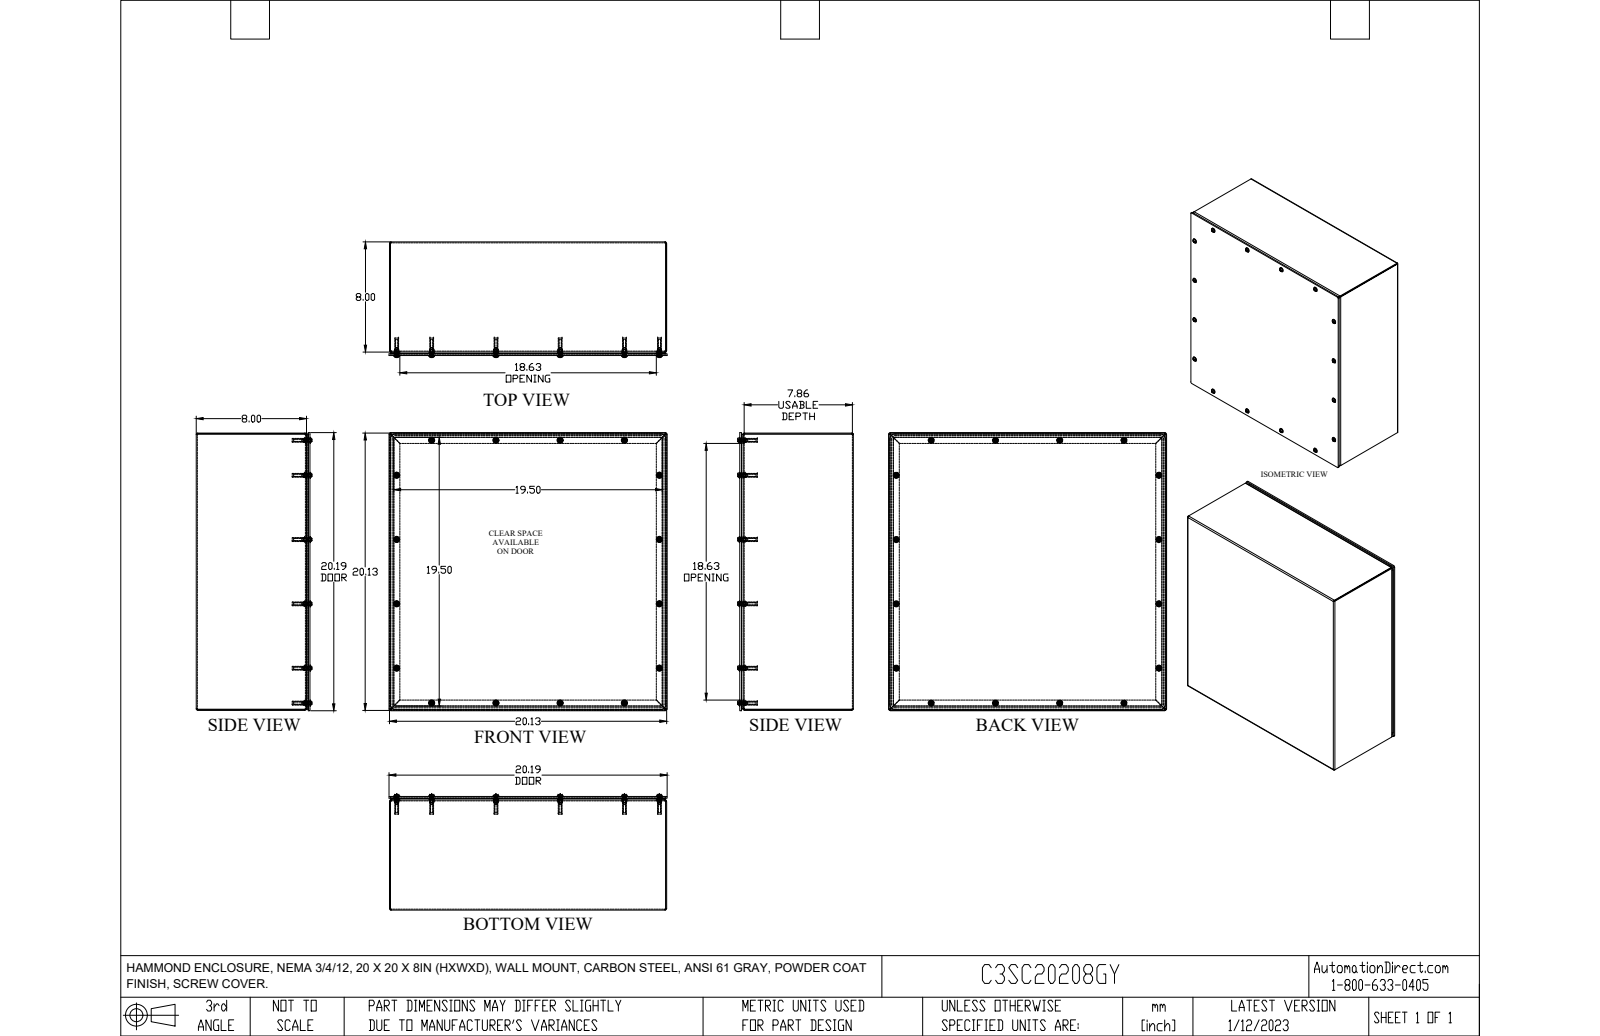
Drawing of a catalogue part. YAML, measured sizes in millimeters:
part_name: "C3SC20208GY"
step_written_by: "SolidWorks 2021 (AUTOMOTIVE_DESIGN)"
units: millimeters
bodies: {solids: 51, faces: 1476, planar: 920, cylindrical: 272, other: 284}
overall_size: [512.8, 512.8, 213.4]
volume: 2129000
surface_area: 2028000
round_holes:
  - {diameter: 4, count: 16}
  - {diameter: 4.1, count: 16}
  - {diameter: 6.4, count: 16}
round_bosses_or_shafts:
  - {diameter: 11.2, count: 16}
  - {diameter: 9.9, count: 16}
  - {diameter: 7, count: 16}
  - {diameter: 6.1, count: 16}
  - {diameter: 4.8, count: 16}
  - {diameter: 3.8, count: 16}
partial_cylinders:
  - {radius: 4.1, count: 16}
  - {radius: 1, count: 8}
  - {radius: 2.8, count: 8}
  - {radius: 3.2, count: 8}
  - {radius: 3.2, count: 4}
  - {radius: 9.5, count: 4}
face_to_face_distances: [1.8, 3.2, 207.8, 204.6, 209.6, 206.4, 511.3, 509.5, 1.8, 507.7]
hole_center_spacings: [498.8, 118.5, 194, 237.1, 308.3, 352.7, 425, 458.2]
